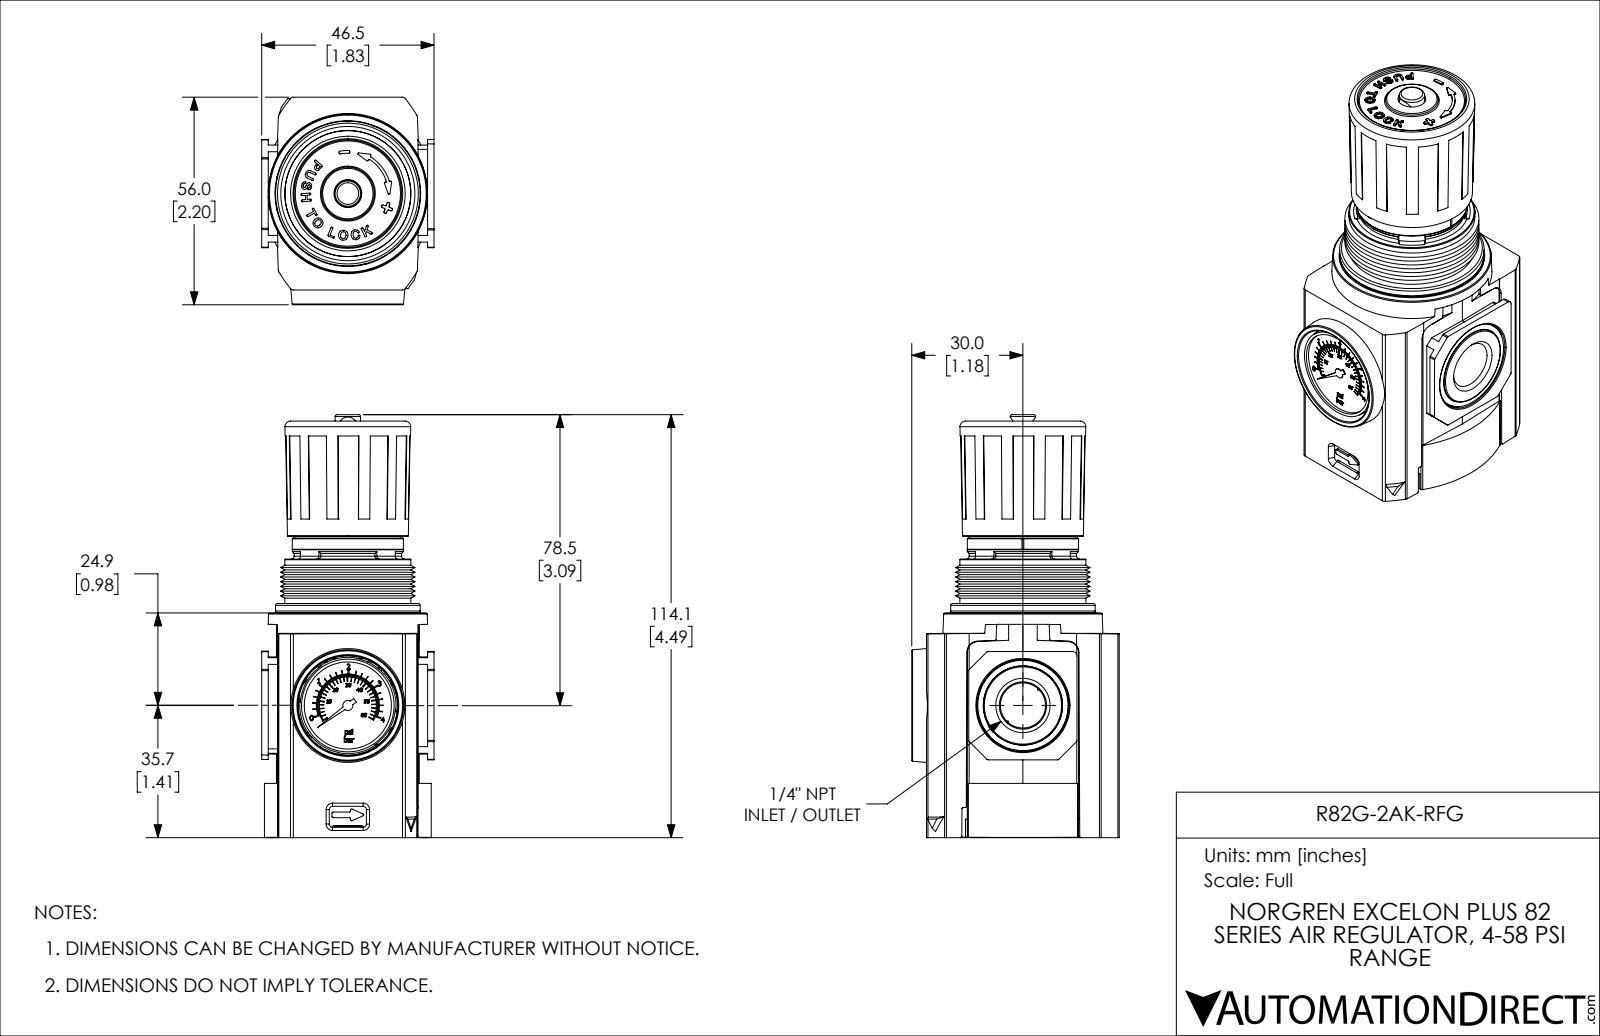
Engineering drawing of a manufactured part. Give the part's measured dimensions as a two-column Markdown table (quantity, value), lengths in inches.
| quantity | value |
| --- | --- |
| part name | R82G-2AK-RFG |
| STEP written by | SolidWorks 2021 (CONFIG_CONTROL_DESIGN) |
| units | inches |
| bodies | 5 solids, 2012 faces (726 planar, 959 cylindrical, 327 other) |
| overall size | 4.492 × 2.205 × 1.831 |
| volume | 8.932 in³ |
| surface area | 86.75 in² |
| round holes (diameter × count) | 0.097 × 4, 0.138 × 2, 0.128 × 1, 0.197 × 1, 0.236 × 1, 0.886 × 1, 0.925 × 1, 1.102 × 1, 1.354 × 1 |
| round bosses / shafts (diameter × count) | 0.224 × 2, 0.118 × 2, 1.535 × 1, 1.339 × 1, 1.181 × 1, 1.161 × 1, 1.138 × 1, 1.098 × 1 |
| partial cylindrical surfaces (radius × count) | 0.039 × 68, 0.02 × 39, 0.009 × 25, 0.006 × 12, 0.012 × 12, 0.031 × 12, 0.118 × 10, 0.01 × 9 |
| main face-to-face distances | 0.059, 1.988, 0.182, 1.352, 0.354, 1.417, 1.475, 0.123, 1.293, 1.169 |
| hole center spacings | 0.63, 1.091, 1.26, 2.705, 3.325, 2.965 |
